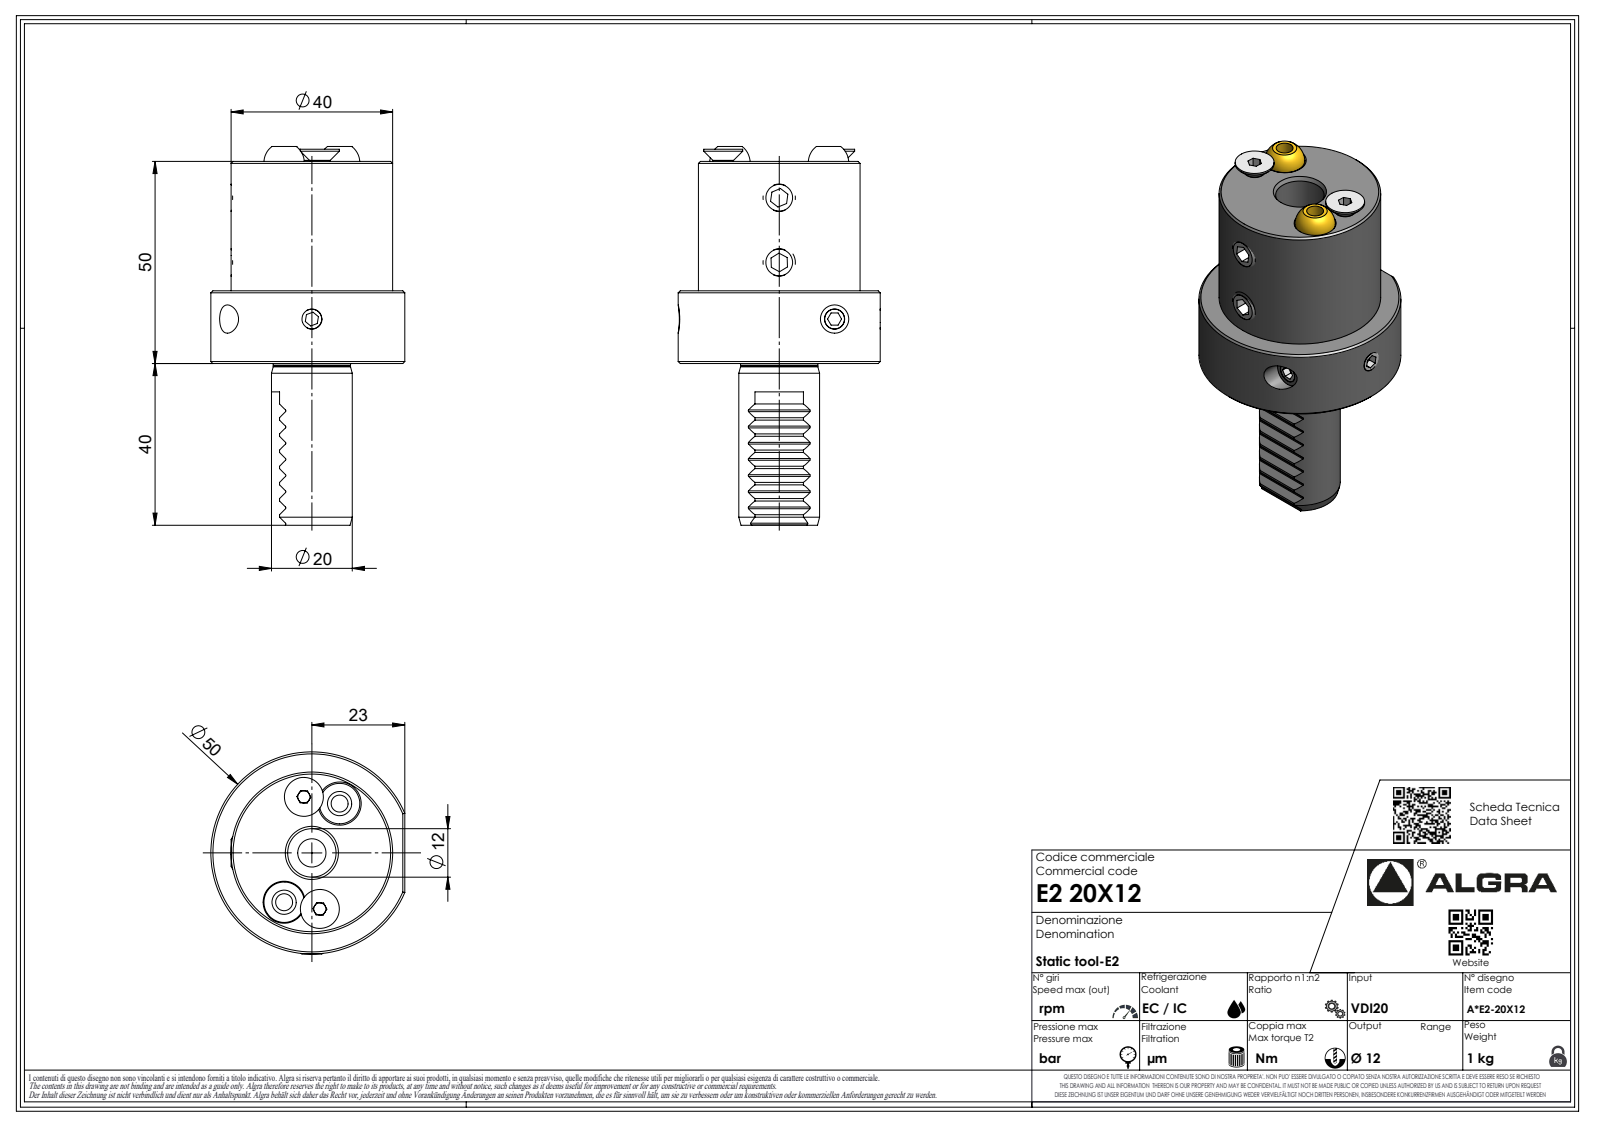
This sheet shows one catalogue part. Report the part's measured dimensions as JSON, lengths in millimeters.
{"part_name": "E220X12", "step_written_by": "SolidWorks 2023 (AUTOMOTIVE_DESIGN)", "units": "millimeters", "bodies": {"solids": 1, "faces": 260, "planar": 179, "cylindrical": 39, "other": 42}, "overall_size": [93.7, 50, 48], "volume_mm3": 83357, "surface_area_mm2": 15373, "round_holes": [[1.05, 1], [12, 1]], "round_bosses_or_shafts": [[50, 1], [40, 1], [20, 1], [19.1, 1], [3.18, 1], [0.85, 1]], "partial_cylinders_radius": [[0.3, 8], [0.17, 7], [0.26, 7], [1.85, 7], [0.1, 1]], "face_to_face_distances": [50, 18, 32, 2.83, 40, 58, 90, 5.66, 5.65, 14.14]}
